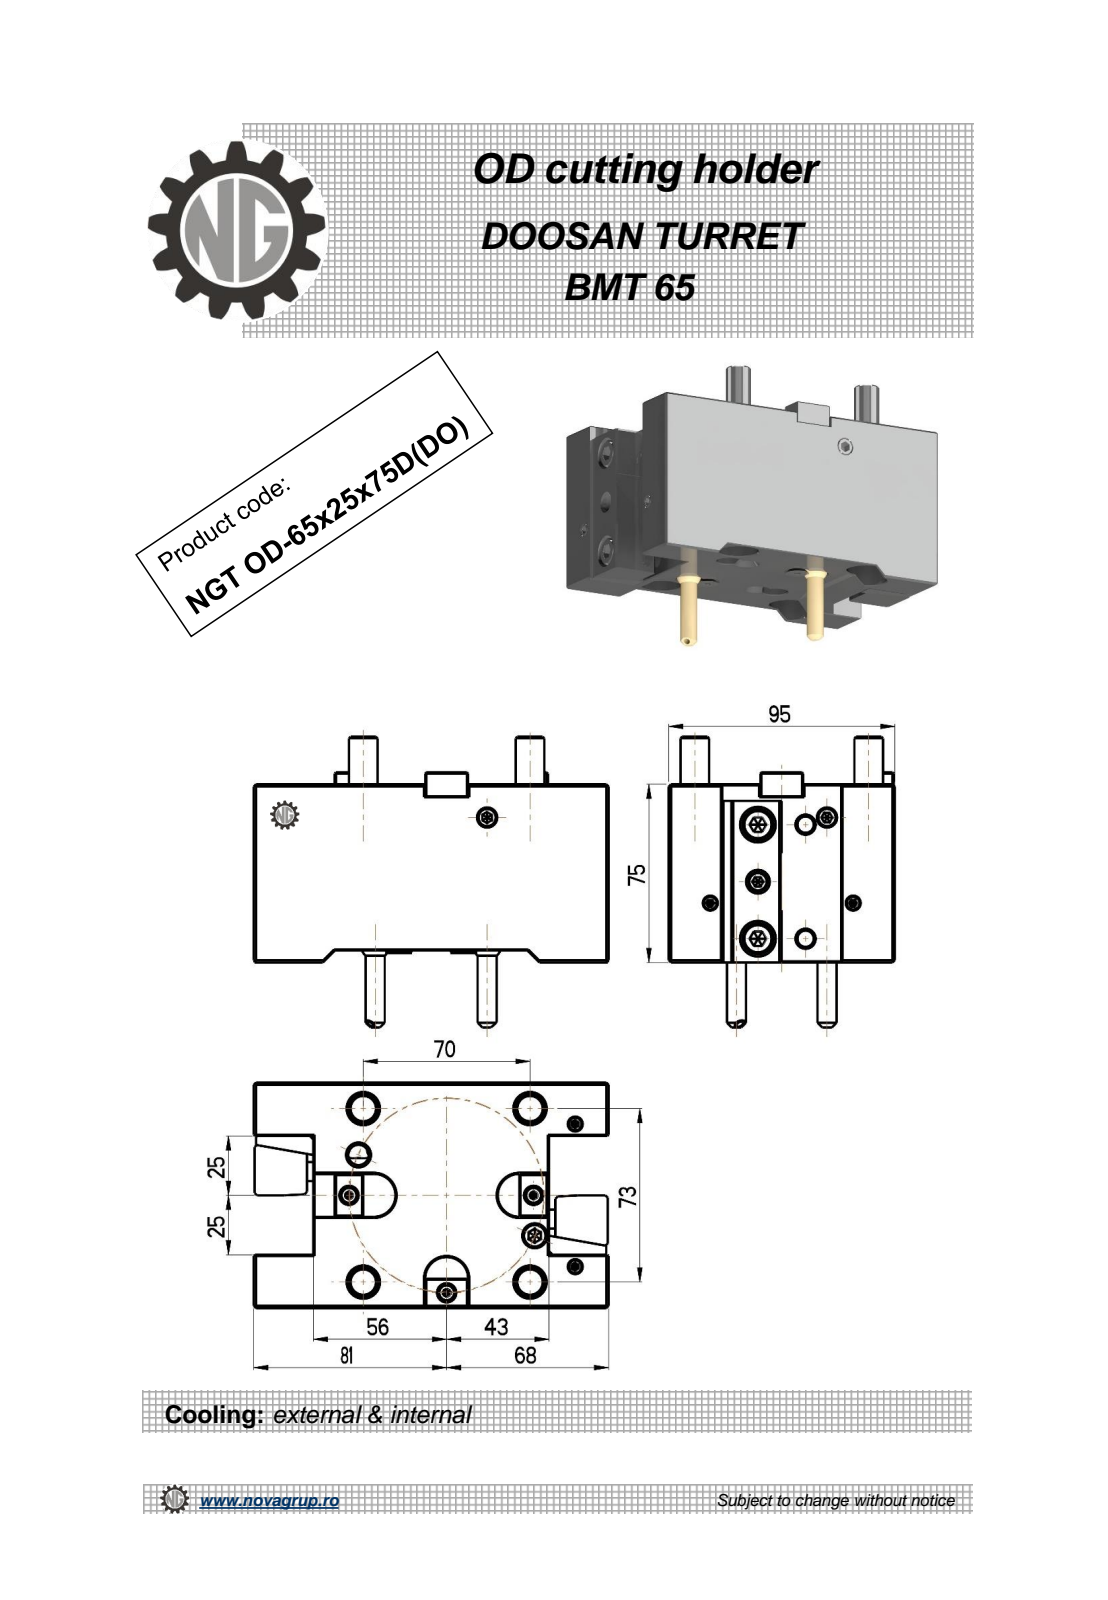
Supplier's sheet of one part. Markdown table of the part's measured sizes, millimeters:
| quantity | value |
| --- | --- |
| part name | NGT_OD_65_25_75D_DO |
| STEP written by | PRO/ENGINEER BY PARAMETRIC TECHNOLOGY CORPORATION, 2010280 (CONFIG_CONTROL_DESIGN) |
| units | millimeters |
| bodies | 1 solid, 307 faces (207 planar, 57 cylindrical, 43 other) |
| overall size | 149 × 122.34 × 95 |
| volume | 919 994 mm³ |
| surface area | 81 667 mm² |
| round holes (diameter × count) | 3 × 2, 5 × 2, 8.5 × 1 |
| round bosses / shafts (diameter × count) | 8 × 8, 12 × 4, 11.2 × 2 |
| partial cylindrical surfaces (radius × count) | 0.22 × 12, 0.51 × 6, 9 × 3 |
| main face-to-face distances | 95, 25, 70, 124, 5, 75, 22.5, 72.5, 149, 99 |
| hole center spacings | 7.28, 60.44, 64.9 |
